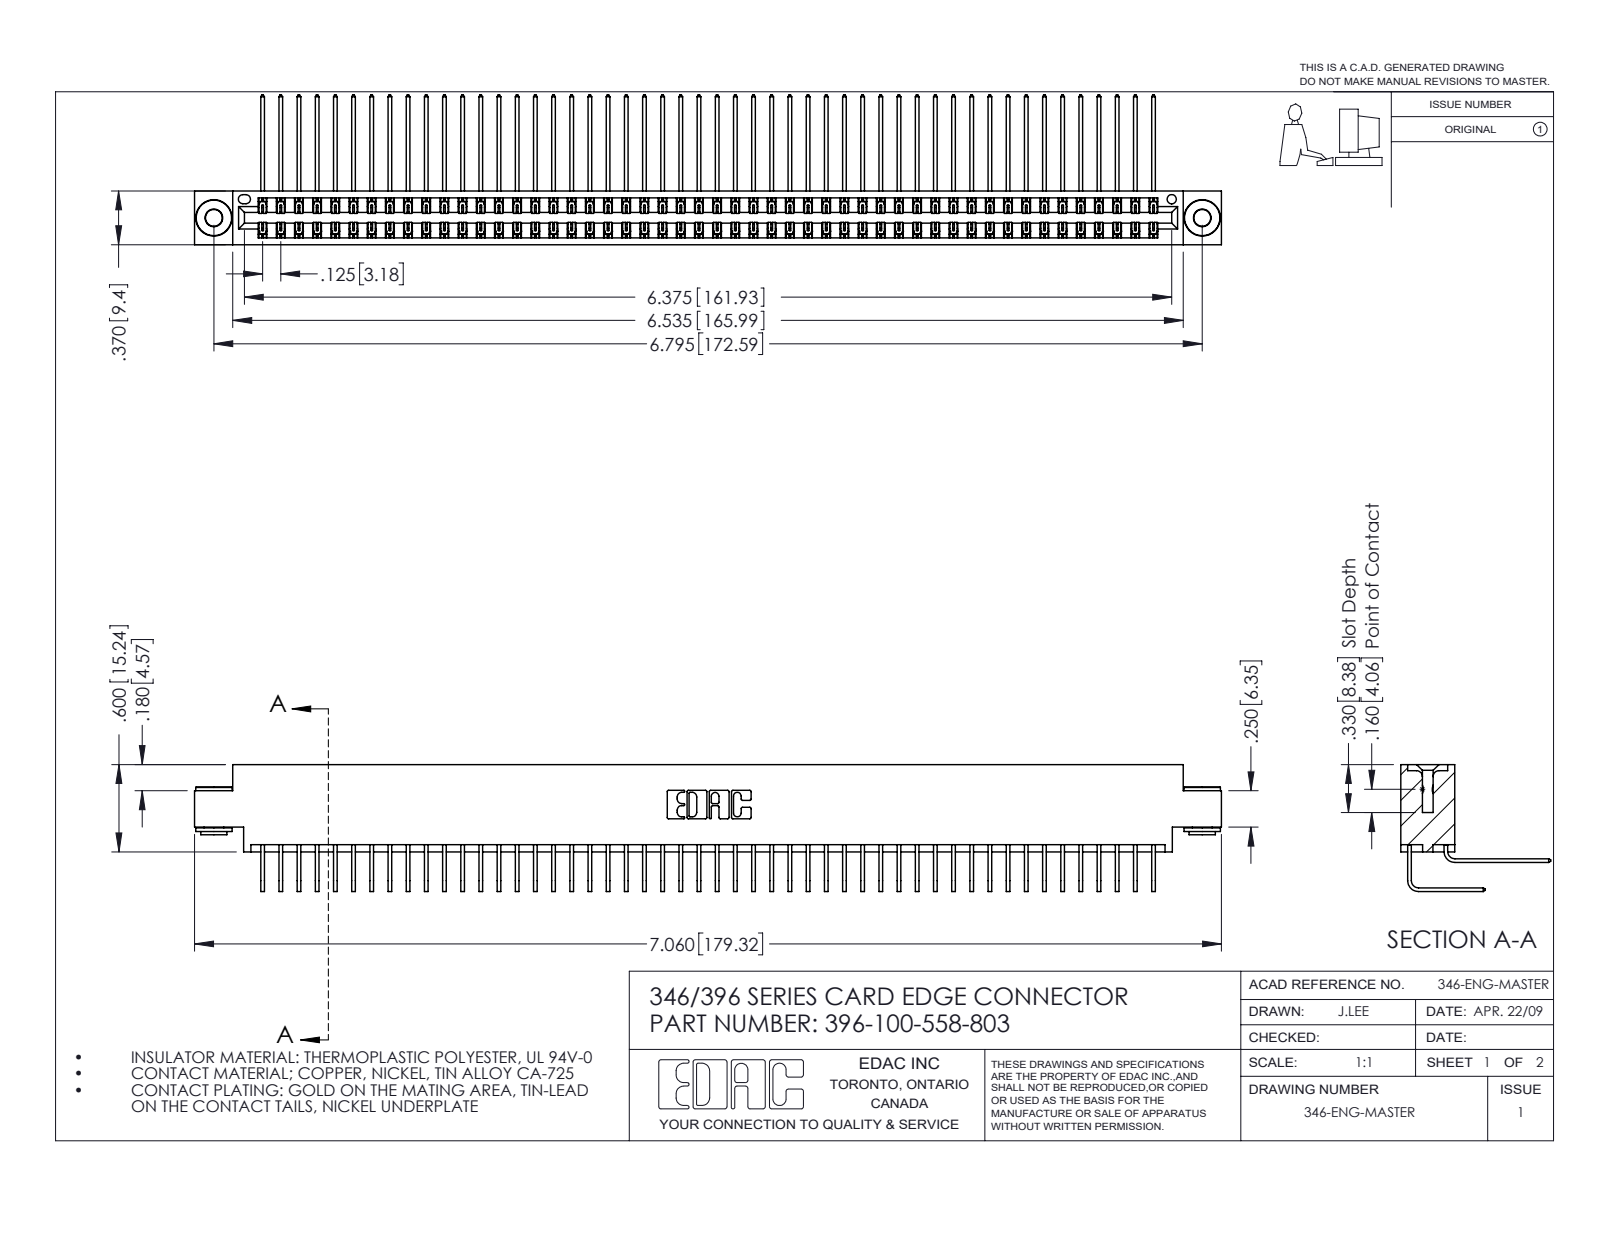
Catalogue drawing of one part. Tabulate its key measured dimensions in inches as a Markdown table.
| quantity | value |
| --- | --- |
| part name | 345-250-002_345-250-002-102; 396-100-558-803; 345-292-001_558 559 Tail - 1; 345-292-001_558 Tail - 2 (+1 more) |
| STEP written by | SolidWorks 2016 (CONFIG_CONTROL_DESIGN) |
| units | inches |
| bodies | 103 solids, 5564 faces (3790 planar, 1766 cylindrical, 8 other) |
| overall size | 7.06 × 1.03 × 0.873 |
| volume | 1.098 in³ |
| surface area | 43.42 in² |
| round holes (diameter × count) | 0.116 × 2, 0.156 × 2, 0.064 × 1 |
| round bosses / shafts (diameter × count) | 0.25 × 2, 0.18 × 2, 0.136 × 2 |
| partial cylindrical surfaces (radius × count) | 0.006 × 150, 0.01 × 22, 0.007 × 6, 0.031 × 6, 0.026 × 3, 0.014 × 2, 0.022 × 2, 0.024 × 2 |
| main face-to-face distances | 0.322, 0.048, 0.025, 0.37, 0.25, 0.298, 0.072, 0.275, 0.148, 0.222 |
| hole center spacings | 0.246, 6.586, 6.795 |
